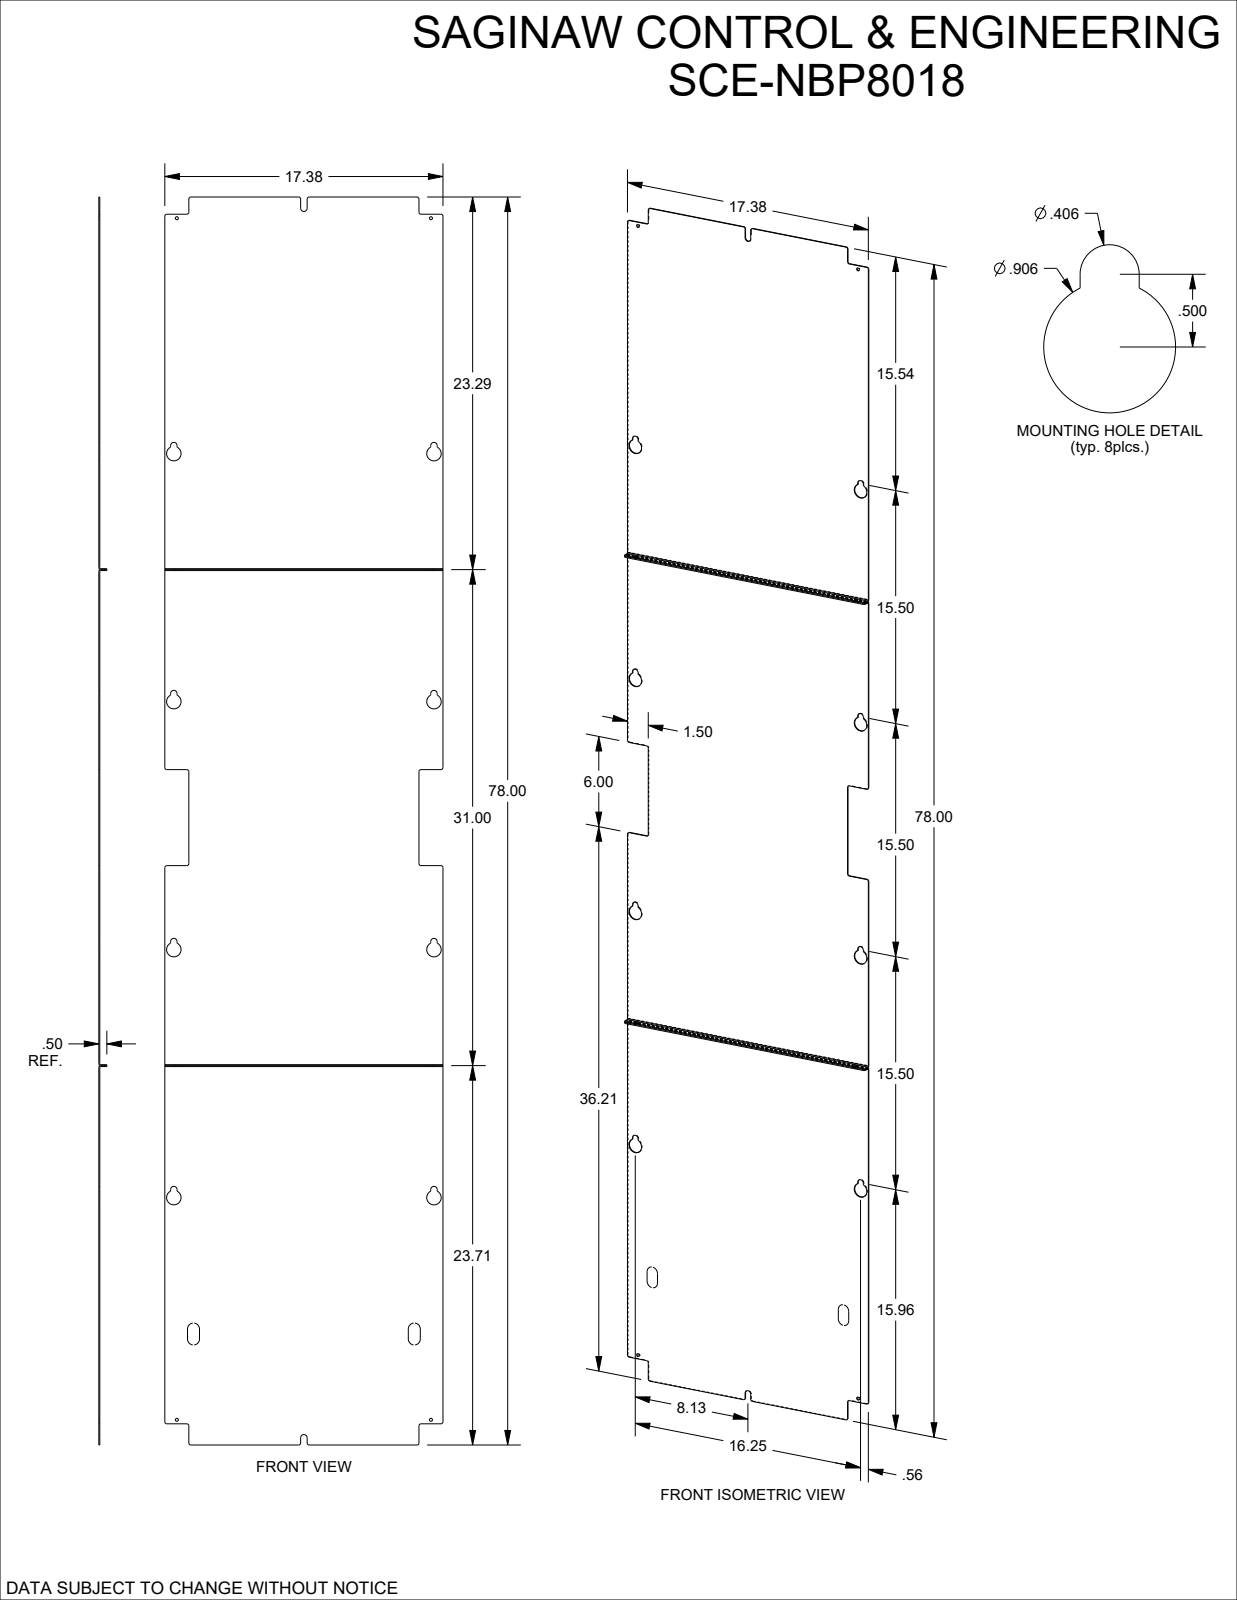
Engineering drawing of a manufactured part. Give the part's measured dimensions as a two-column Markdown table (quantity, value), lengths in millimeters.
| quantity | value |
| --- | --- |
| part name | SCE-NBP8018 |
| STEP written by | SolidWorks 2023 (AUTOMOTIVE_DESIGN) |
| units | millimeters |
| bodies | 3 solids, 174 faces (80 planar, 94 cylindrical, 0 other) |
| overall size | 1981.2 × 441.3 × 12.7 |
| volume | 1 329 000 mm³ |
| surface area | 1 755 000 mm² |
| round holes (diameter × count) | 23 × 8, 4.8 × 6 |
| partial cylindrical surfaces (radius × count) | 3.2 × 26, 0.8 × 12, 5.2 × 10, 1.3 × 4, 2.8 × 4 |
| main face-to-face distances | 1.5, 787.4, 1.5, 3, 788.9, 790.4, 788.9, 785.9, 785.9, 784.4 |
| hole center spacings | 393.7, 570.4, 412.8, 787.4, 889, 403.2, 352.8, 373.7 |
